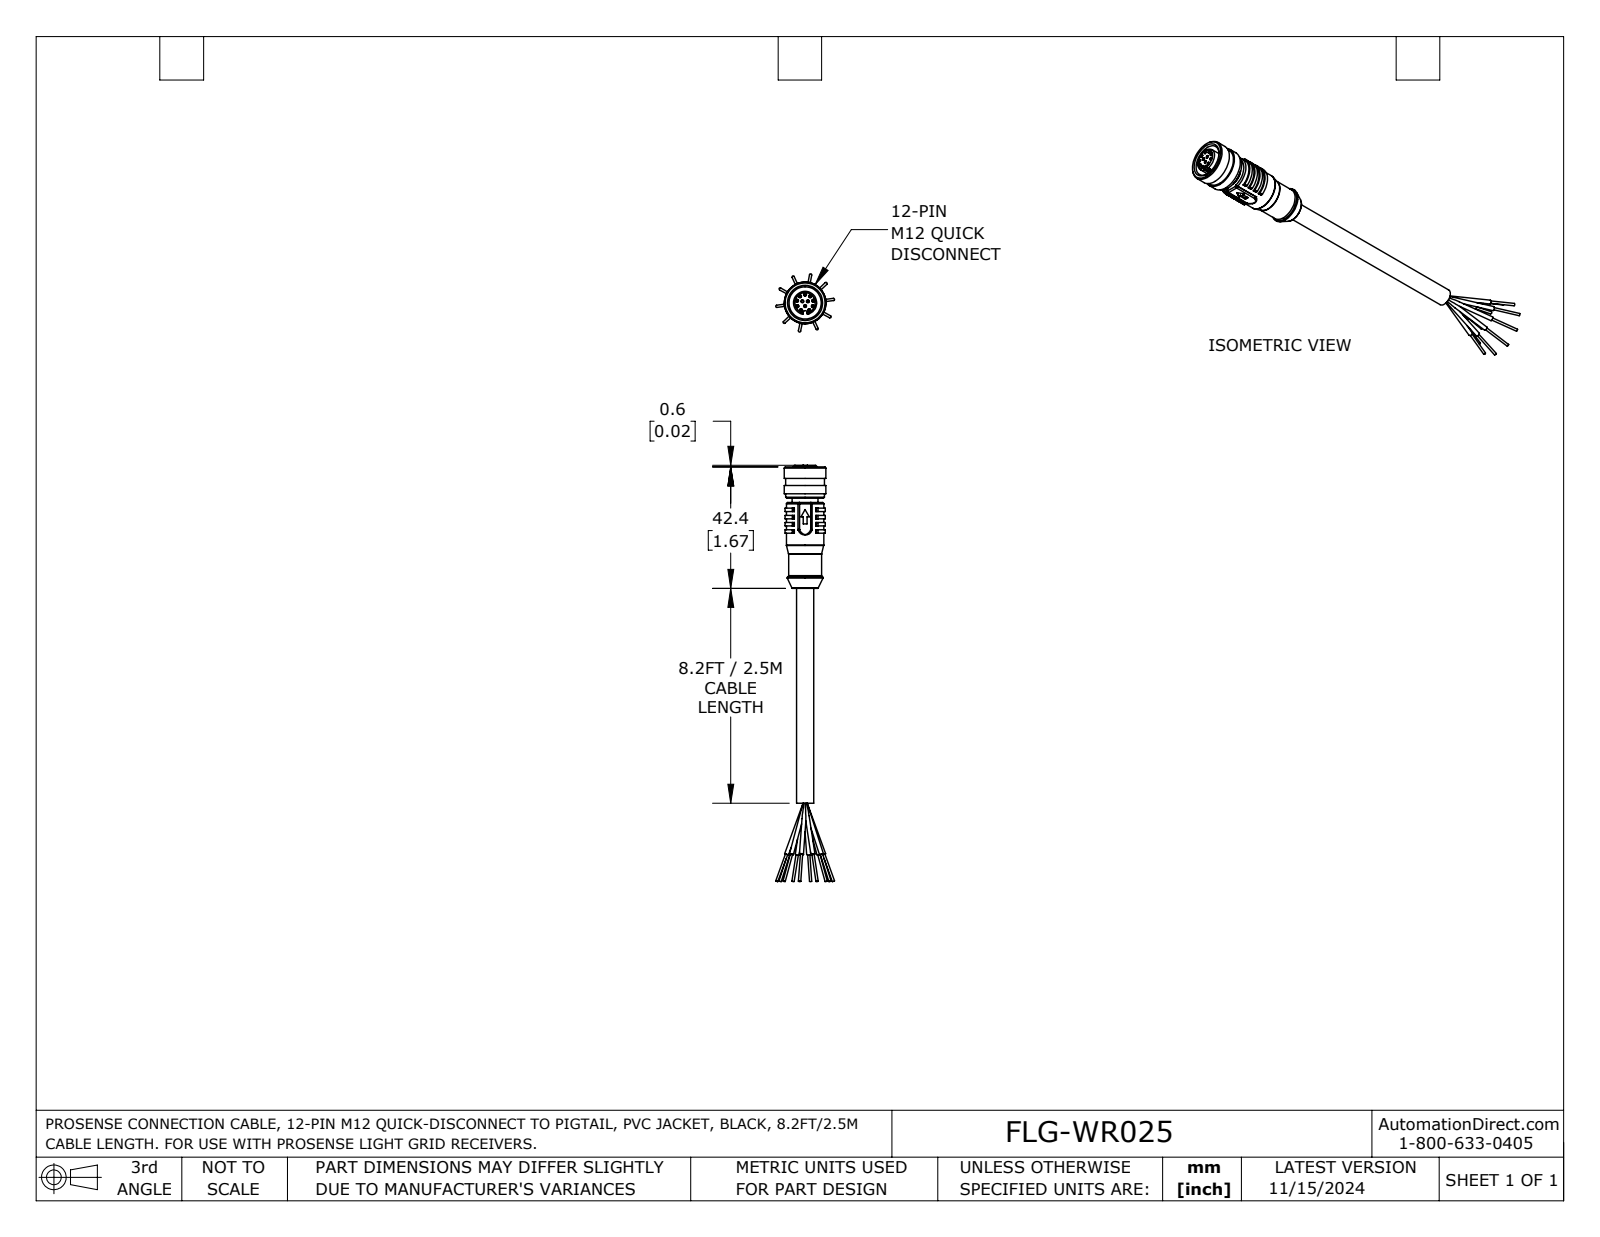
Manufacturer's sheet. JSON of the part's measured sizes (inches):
{"part_name": "FLG-WR-CABLE", "step_written_by": "SolidWorks 2023 (AUTOMOTIVE_DESIGN)", "units": "inches", "bodies": {"solids": 1, "faces": 209, "planar": 90, "cylindrical": 67, "other": 52}, "overall_size": [5.723, 0.81, 0.801], "volume_in3": 0.456, "surface_area_in2": 8.221, "round_holes": [[0.031, 12], [0.443, 1]], "round_bosses_or_shafts": [[0.055, 10], [0.031, 10], [0.572, 1], [0.533, 1], [0.513, 1], [0.454, 1], [0.356, 1], [0.318, 1]], "partial_cylinders_radius": [[0.02, 8], [0.017, 1], [0.099, 1], [0.276, 1], [0.276, 1]], "face_to_face_distances": [0.098, 0.059, 0.295, 0.197, 0.134, 0.193, 0.047, 0.516, 0.319, 0.394], "hole_center_spacings": [0.114, 0.074, 0.19, 0.139, 0.073, 0.221, 0.043, 0.075]}
